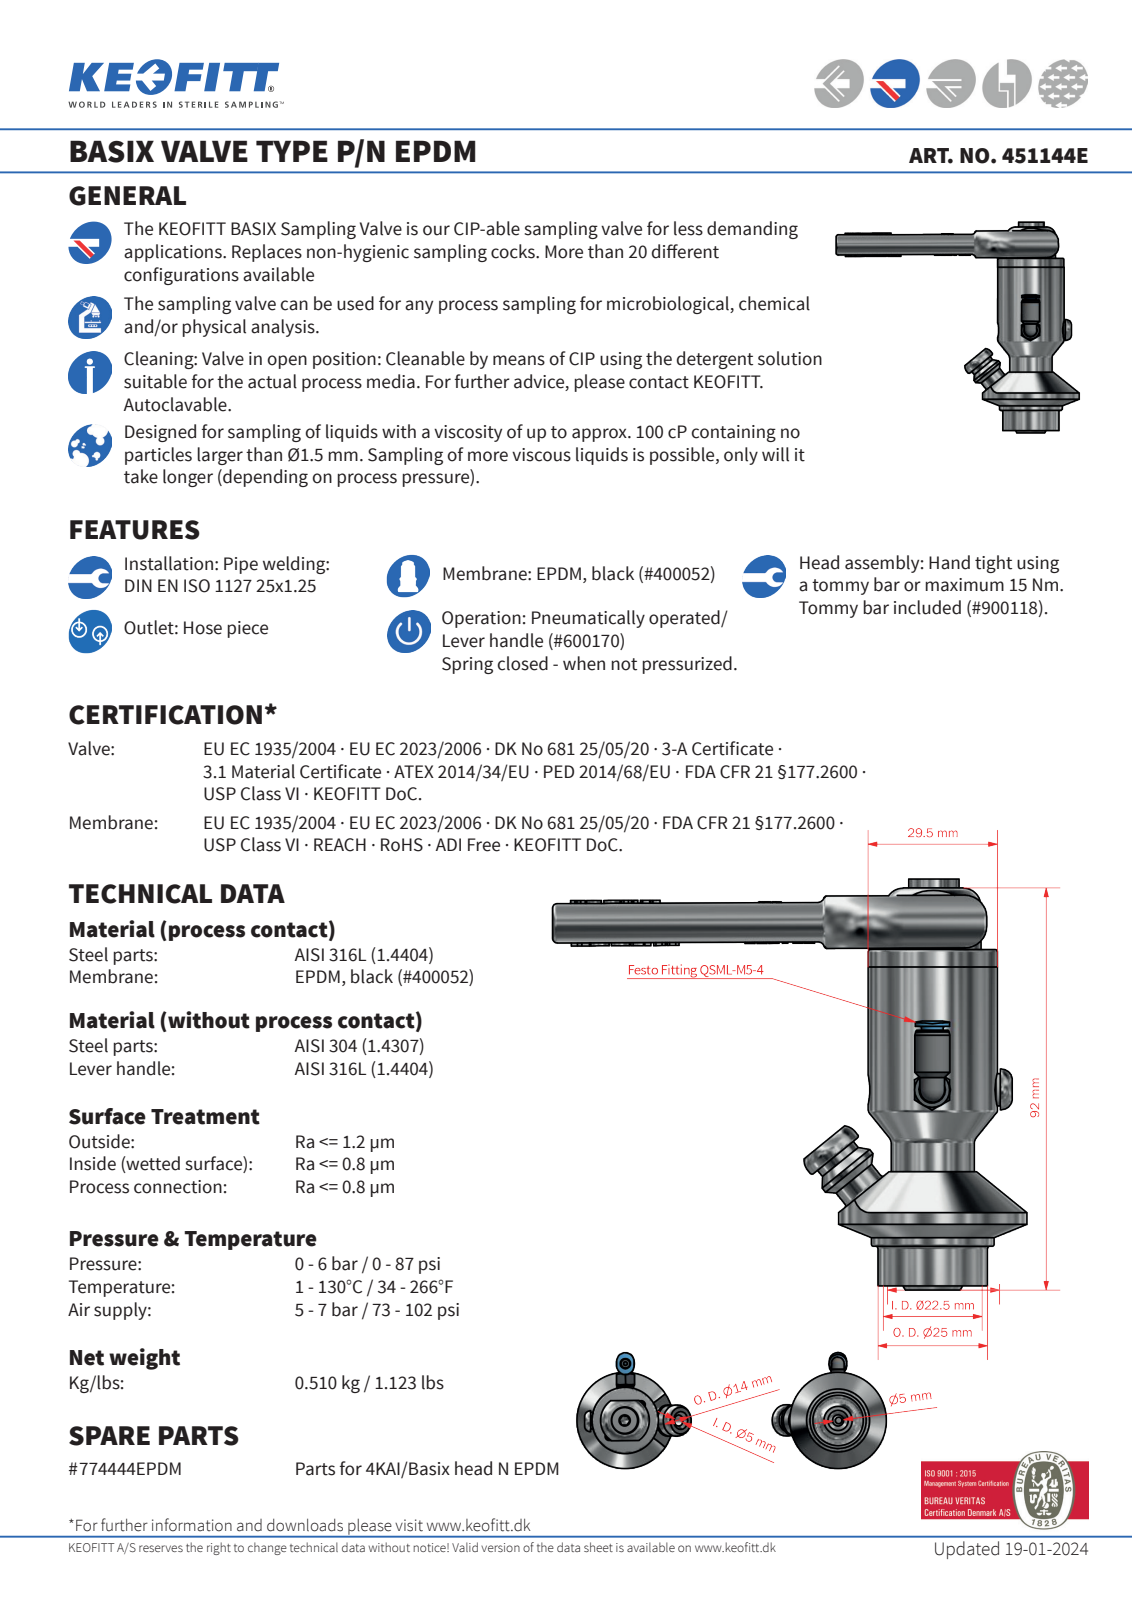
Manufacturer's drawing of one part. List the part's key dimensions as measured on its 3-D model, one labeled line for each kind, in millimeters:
Part name (STEP PRODUCT): 451144E
STEP written by: Autodesk Inventor 2020 (AUTOMOTIVE_DESIGN)
Units: millimetres
Bodies: 3 solids, 719 faces (296 planar, 124 cylindrical, 299 other)
Overall size (bounding box): 116.48 × 91.7 × 51.4
Volume: 68 118 mm³ · Surface area: 24 225 mm²
Round holes (diameter × count): ⌀1.7 ×2, ⌀3 ×2, ⌀4.3 ×2, ⌀5 ×2, ⌀5.05 ×2, ⌀8 ×2, ⌀4 ×1, ⌀6.05 ×1, ⌀10.2 ×1, ⌀12 ×1, ⌀16.5 ×1, ⌀18.5 ×1
Round bosses / shafts (diameter × count): ⌀5 ×3, ⌀16 ×2, ⌀10 ×2, ⌀7.4 ×2, ⌀6.6 ×2, ⌀6 ×2, ⌀5.6 ×2, ⌀43 ×1
Partial cylindrical surfaces — rounded edges, fillets, slot ends (radius × count): R0.5 ×14, R0.52 ×12, R3 ×6, R1 ×2, R1.5 ×2, R3.9 ×2, R5 ×2, R8 ×2
Main face-to-face distances: 1.5, 10.5, 9, 3.1, 12, 4, 2, 19, 14.95, 18.05
Hole centre spacings: 10, 9.95, 10.05, 20
